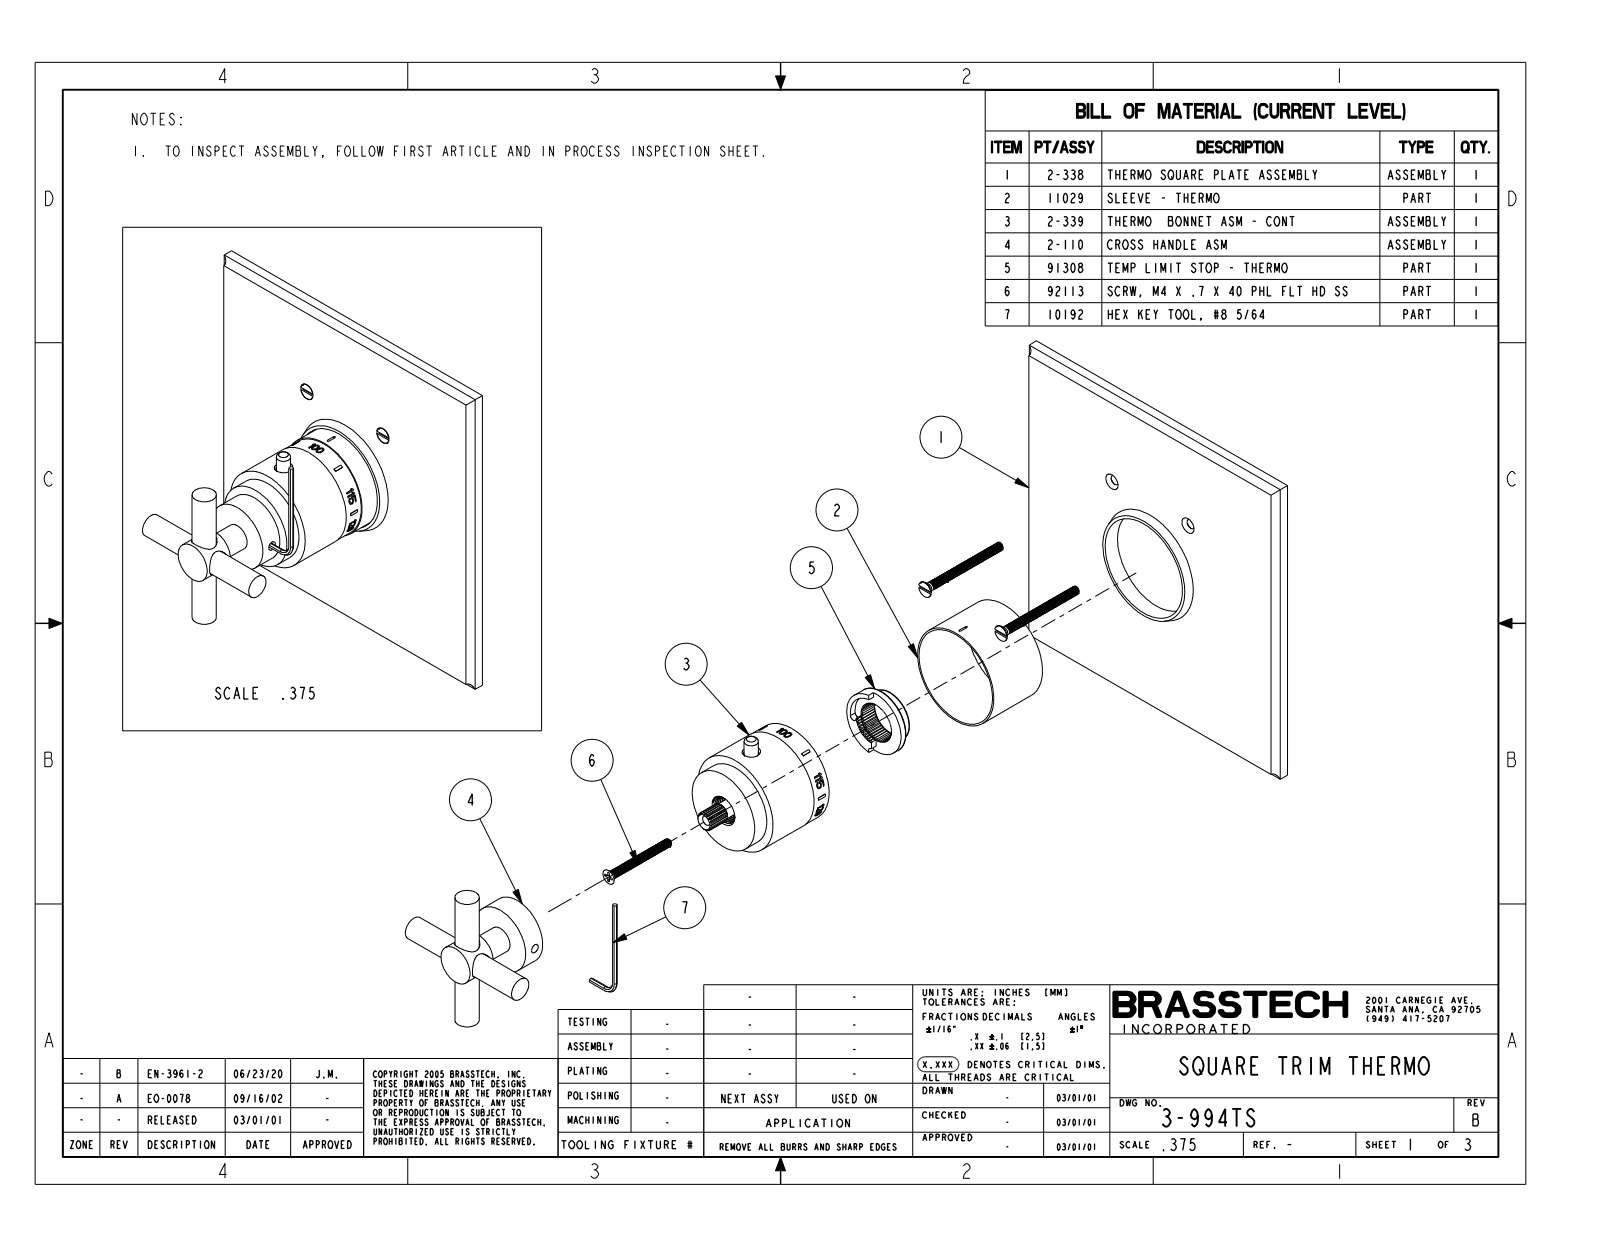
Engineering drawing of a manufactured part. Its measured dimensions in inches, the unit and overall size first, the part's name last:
Units: inches
Overall size (bounding box): 6.5 × 6.5 × 4.254
Round holes (diameter × count): ⌀0.203 ×1, ⌀0.26 ×1
Round bosses / shafts (diameter × count): ⌀0.445 ×2, ⌀1.97 ×1, ⌀1.94 ×1, ⌀1.929 ×1, ⌀1.615 ×1, ⌀1.313 ×1, ⌀0.75 ×1, ⌀0.5 ×1
Partial cylindrical surfaces — rounded edges, fillets, slot ends (radius × count): R0.125 ×4, R0.969 ×1
Main face-to-face distances: 0.313, 6.5, 2.623, 2.31, 2.654, 2.341, 0.031, 3.094, 2.781, 0.471
Volume: 21.09 in³ · Surface area: 119.7 in²
Bodies: 1 solid, 462 faces (341 planar, 89 cylindrical, 32 other)
Part name (STEP PRODUCT): 3-994TS
STEP written by: CREO PARAMETRIC BY PTC INC, 2018400 (CONFIG_CONTROL_DESIGN)
